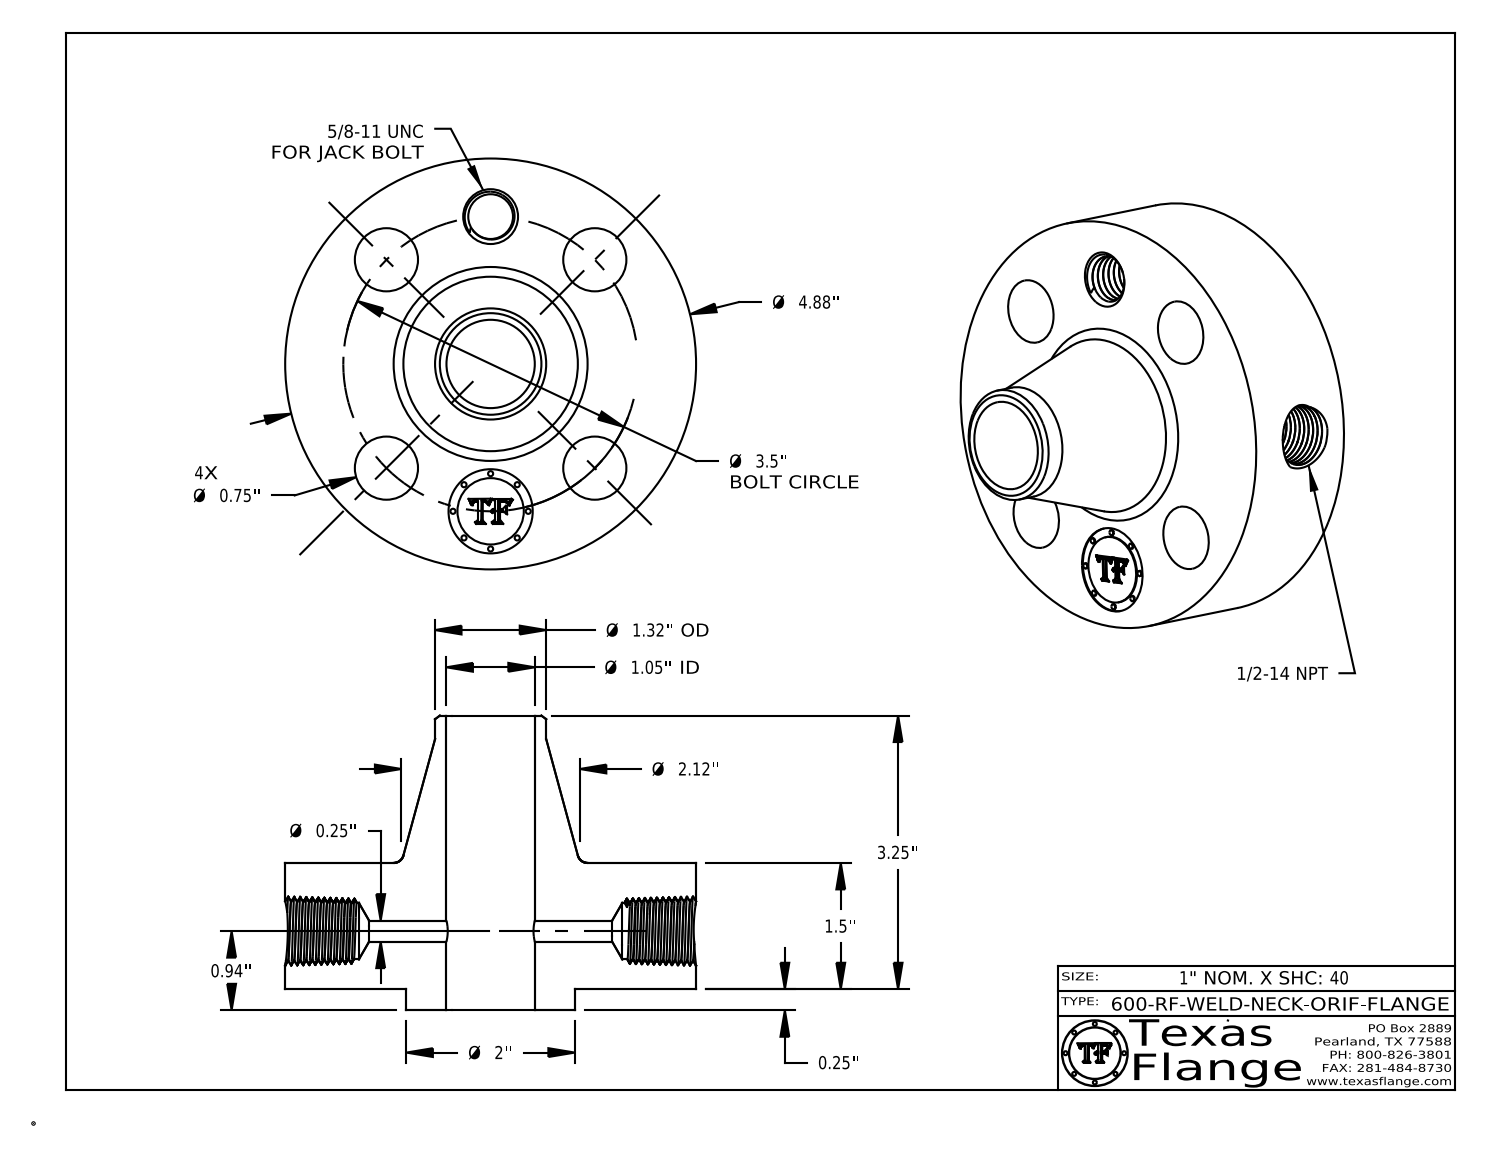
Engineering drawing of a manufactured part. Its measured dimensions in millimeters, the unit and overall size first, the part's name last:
Units: millimetres
Overall size (bounding box): 124 × 124 × 88.9
Round holes (diameter × count): ⌀19.1 ×4, ⌀6.4 ×1, ⌀13.5 ×1, ⌀17.1 ×1, ⌀25.4 ×1, ⌀26.6 ×1
Round bosses / shafts (diameter × count): ⌀1.5 ×8, ⌀124 ×1, ⌀50.8 ×1, ⌀33.5 ×1, ⌀20 ×1
Main face-to-face distances: 38.1, 44.5, 6.4, 44.1, 37.7, 0.4, 88.9, 82.6, 44.8, 7.6
Hole centre spacings: 44.5, 34, 62.9, 82.1, 88.9
Volume: 422 100 mm³ · Surface area: 65 230 mm²
Bodies: 1 solid, 764 faces (369 planar, 87 cylindrical, 308 other)
Part name (STEP PRODUCT): 600-RF-WELD-NECK
STEP written by: CATIA V5 STEP AP214 (AUTOMOTIVE_DESIGN)
